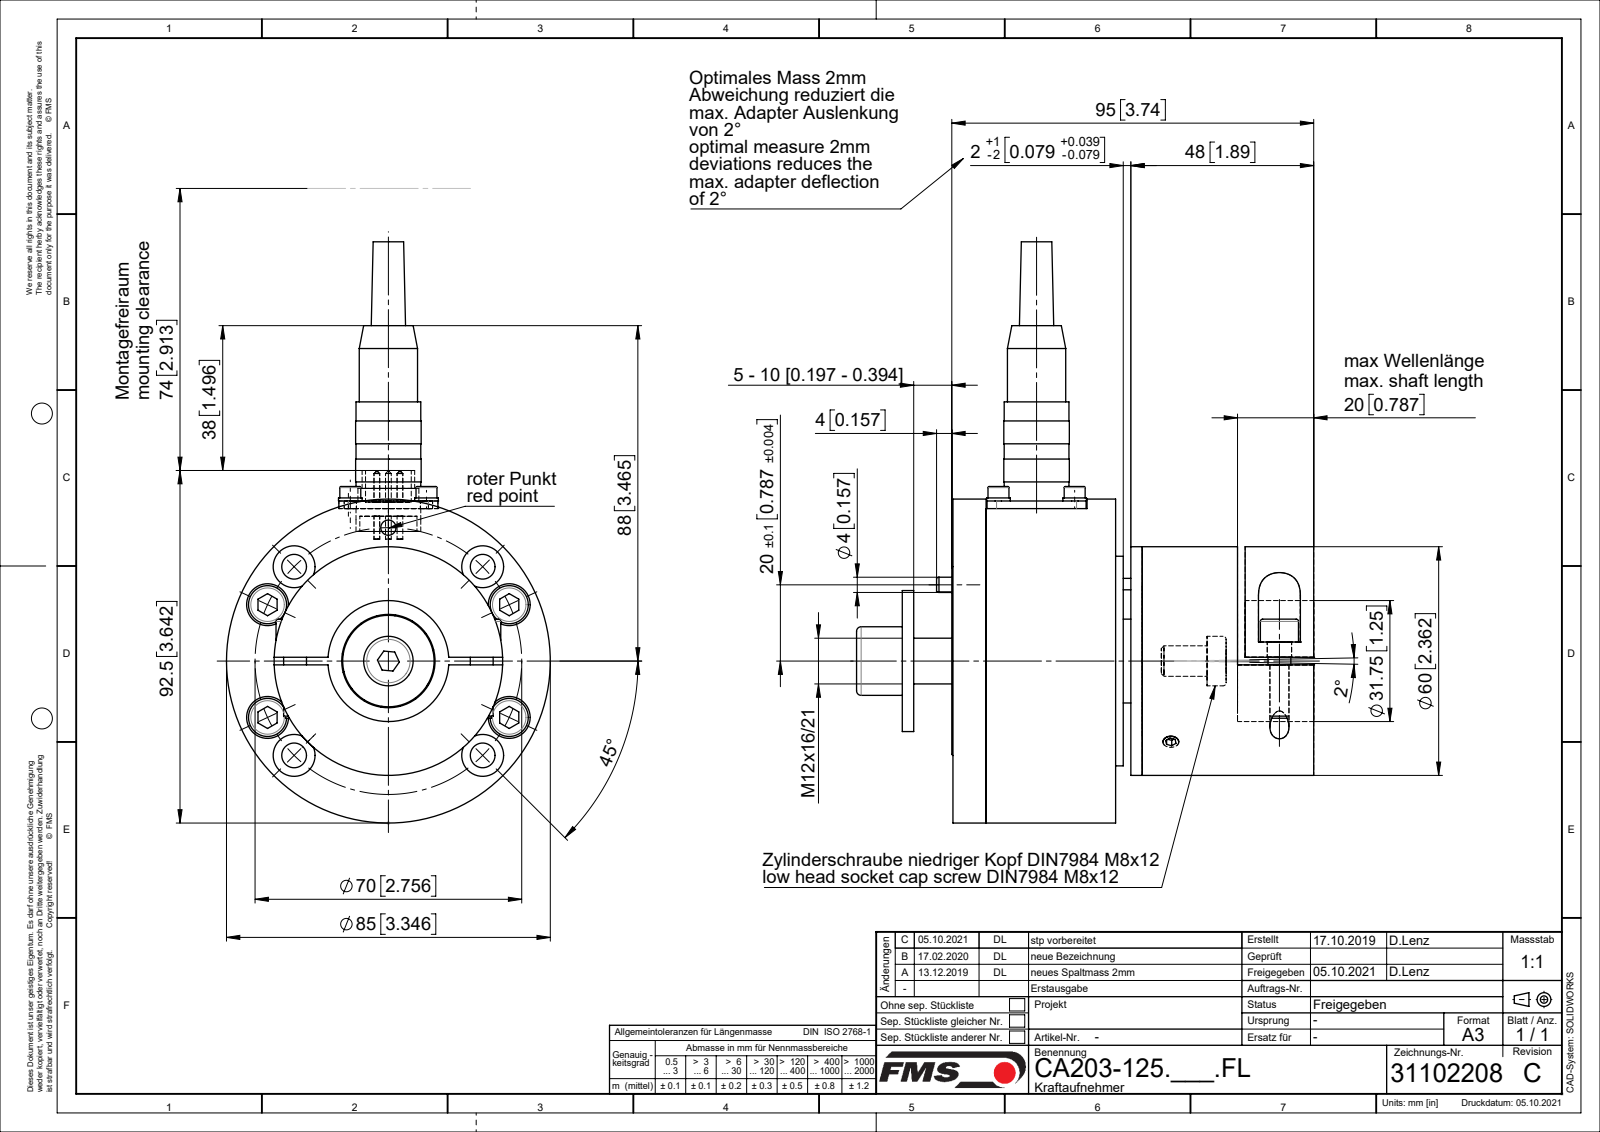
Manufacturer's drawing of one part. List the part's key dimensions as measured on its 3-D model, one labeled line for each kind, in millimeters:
Part name (STEP PRODUCT): 070907-2_01; 31102208_C; Sch DIN9021_M8; Kabeldose_M14x1_Mini_5pol (+8 more)
STEP written by: SolidWorks 2018 (CONFIG_CONTROL_DESIGN)
Units: millimetres
Bodies: 43 solids, 785 faces (270 planar, 326 cylindrical, 189 other)
Overall size (bounding box): 152.5 × 120 × 85
Volume: 307 051 mm³ · Surface area: 111 613 mm²
Round holes (diameter × count): ⌀2.5 ×8, ⌀6.5 ×8, ⌀11 ×8, ⌀5 ×6, ⌀4 ×5, ⌀3.1 ×4, ⌀3.2 ×4, ⌀3.6 ×4, ⌀7 ×4, ⌀3 ×2, ⌀6.4 ×2, ⌀4.2 ×1
Round bosses / shafts (diameter × count): ⌀3 ×8, ⌀6 ×7, ⌀10 ×6, ⌀1.5 ×5, ⌀6.2 ×4, ⌀5.7 ×4, ⌀5.5 ×4, ⌀85 ×1
Partial cylindrical surfaces — rounded edges, fillets, slot ends (radius × count): R2.5 ×4, R5 ×2, R5.5 ×2
Main face-to-face distances: 2, 41, 45, 10, 30, 3, 50, 22, 60, 34
Hole centre spacings: 35, 20, 24.78, 25.2, 32.8, 51.14, 56.46, 28.28
